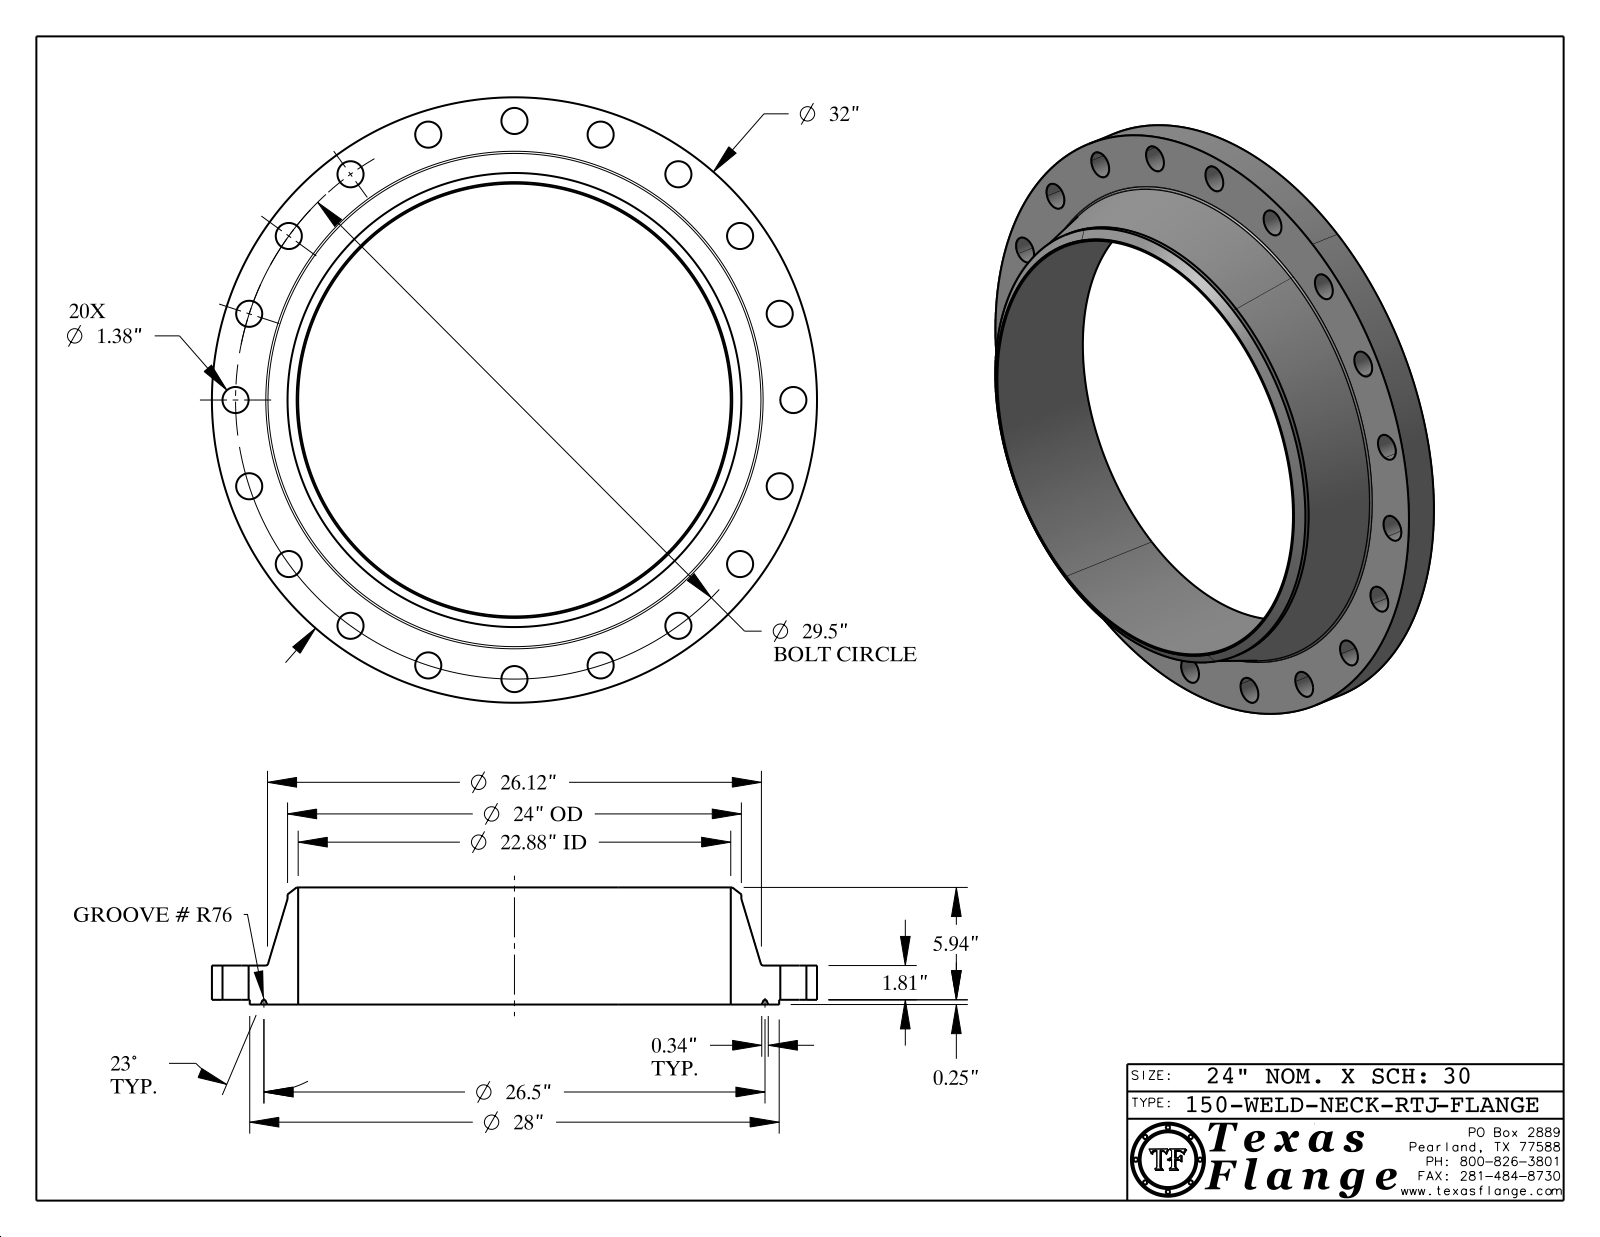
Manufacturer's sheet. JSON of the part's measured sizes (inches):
{"part_name": "150-WELD-NECK-RTJ", "step_written_by": "CATIA V5 STEP AP214 (AUTOMOTIVE_DESIGN)", "units": "inches", "bodies": {"solids": 1, "faces": 453, "planar": 371, "cylindrical": 68, "other": 14}, "overall_size": [32, 32, 6.19], "volume_in3": 1013, "surface_area_in2": 1790, "round_holes": [[1.38, 20], [0.495, 1], [22.876, 1]], "round_bosses_or_shafts": [[0.03, 8], [32, 1], [28, 1], [24, 1], [0.39, 1]], "face_to_face_distances": [2.06, 0.25, 1.81, 6.19, 5.94, 4.13, 2.055, 1.805, 4.135, 0.148], "hole_center_spacings": [14.75, 29.137, 4.615, 17.34, 20.859, 23.866, 26.285, 9.116]}
